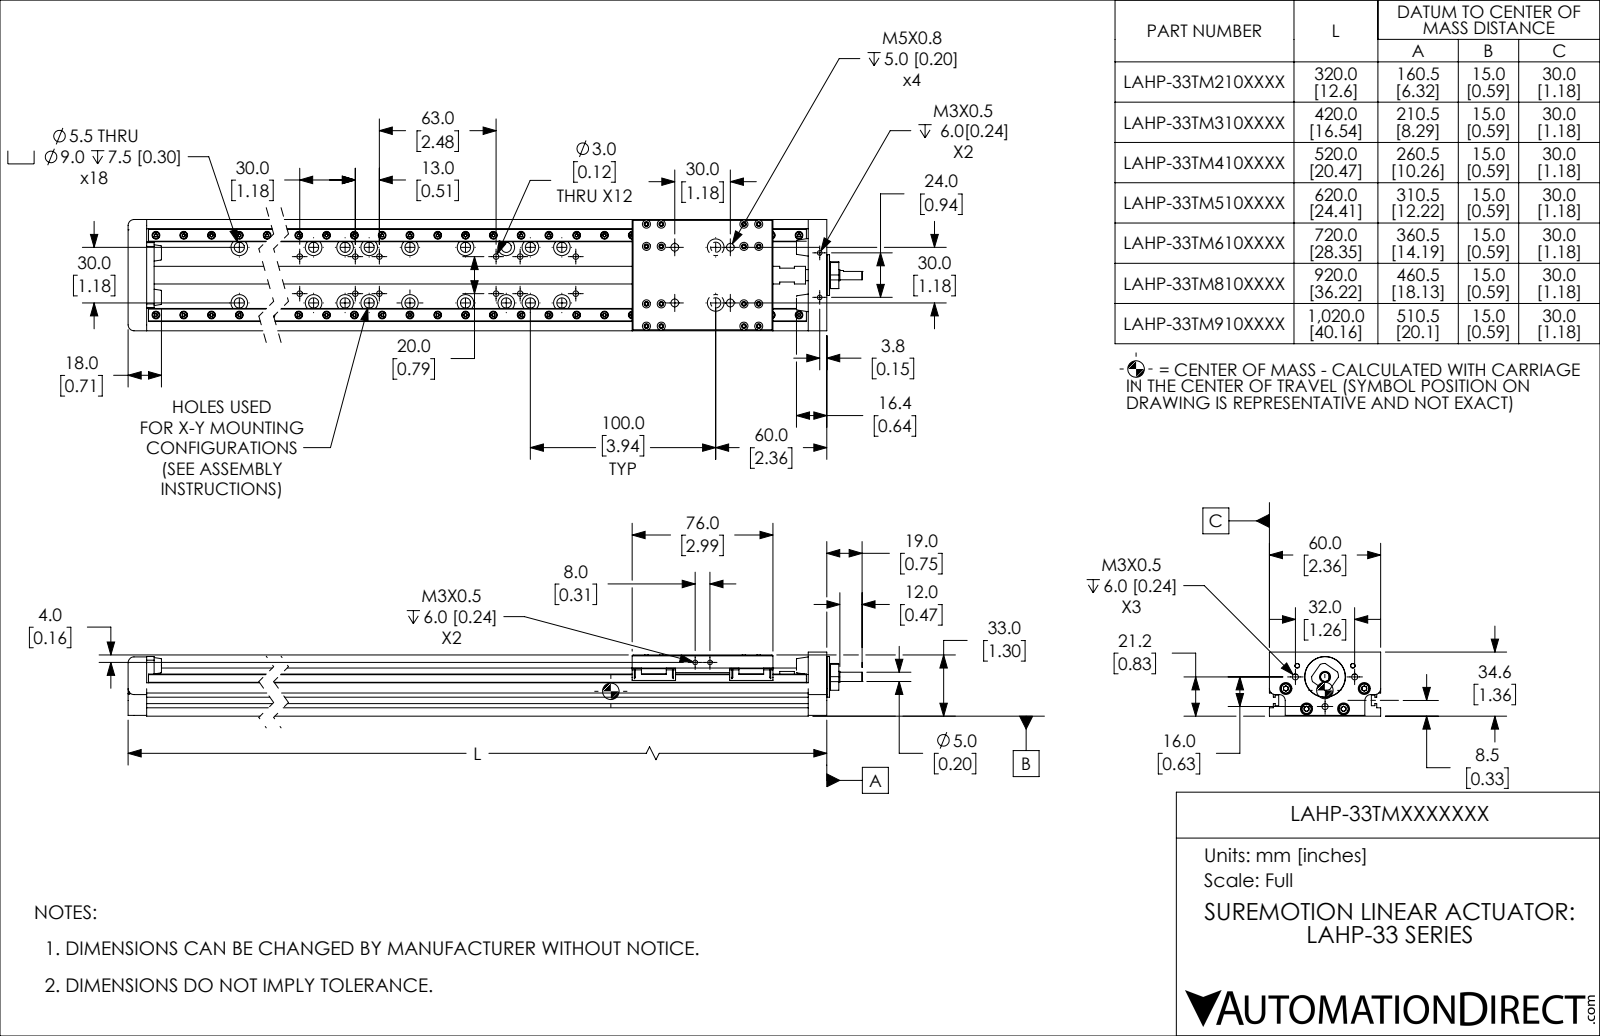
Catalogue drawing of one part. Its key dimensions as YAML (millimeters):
part_name: "LAHP-33TM210LP25; LAHP-33TM210LP25_BASE; LAHP-33TM210LP25_CARRIAGE"
step_written_by: "SolidWorks 2019 (CONFIG_CONTROL_DESIGN)"
units: millimeters
bodies: {solids: 2, faces: 2926, planar: 1362, cylindrical: 901, other: 663}
overall_size: [339.1, 60, 34.6]
volume: 331300
surface_area: 122300
round_holes:
  - {diameter: 4.2, count: 44}
  - {diameter: 1.6, count: 42}
  - {diameter: 2.4, count: 40}
  - {diameter: 5.5, count: 18}
  - {diameter: 9, count: 18}
  - {diameter: 1.6, count: 16}
  - {diameter: 2.6, count: 16}
  - {diameter: 4.4, count: 16}
  - {diameter: 2.5, count: 14}
  - {diameter: 3, count: 14}
  - {diameter: 3.6, count: 8}
  - {diameter: 6.5, count: 8}
round_bosses_or_shafts:
  - {diameter: 3.8, count: 40}
  - {diameter: 2, count: 40}
  - {diameter: 5.5, count: 12}
  - {diameter: 3, count: 12}
  - {diameter: 5.7, count: 2}
  - {diameter: 22, count: 1}
  - {diameter: 14.5, count: 1}
  - {diameter: 10, count: 1}
partial_cylinders:
  - {radius: 3.2, count: 16}
  - {radius: 0.2, count: 8}
  - {radius: 0.5, count: 8}
  - {radius: 0.9, count: 4}
  - {radius: 0.3, count: 2}
  - {radius: 7.3, count: 1}
face_to_face_distances: [7.8, 7, 12, 48, 43, 5, 55, 10.3, 33, 25.1]
hole_center_spacings: [30, 20, 9, 15, 26.1, 52, 59.7, 60]
